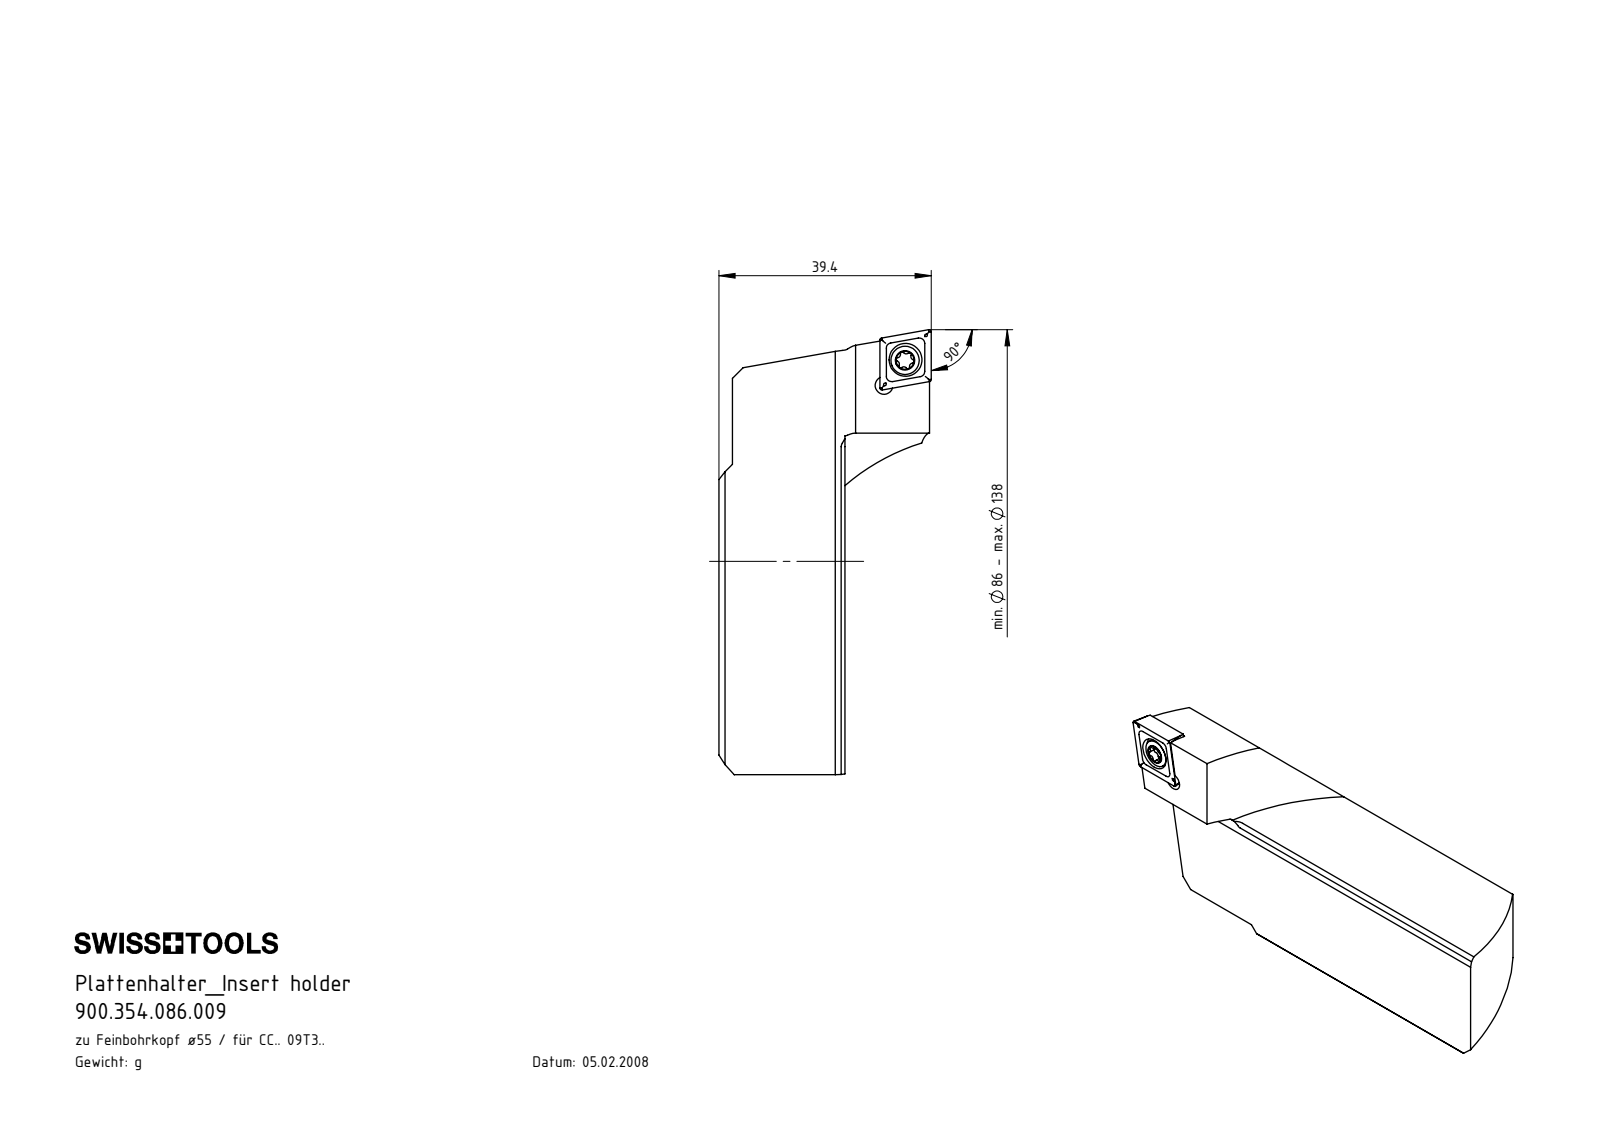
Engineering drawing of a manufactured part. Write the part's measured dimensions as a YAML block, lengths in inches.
part_name: "900.354.086.009; CCMT09T304; WCB-ER2.001.009_A; F00-WCB.086.001_C"
step_written_by: "SolidWorks 2017 (CONFIG_CONTROL_DESIGN)"
units: inches
bodies: {solids: 3, faces: 382, planar: 226, cylindrical: 39, other: 117}
overall_size: [3.251, 1.551, 1.077]
volume: 2.048
surface_area: 13.91
round_holes:
  - {diameter: 0.13, count: 2}
  - {diameter: 0.173, count: 1}
  - {diameter: 0.24, count: 1}
round_bosses_or_shafts:
  - {diameter: 0.207, count: 1}
  - {diameter: 0.157, count: 1}
partial_cylinders:
  - {radius: 0.008, count: 8}
  - {radius: 0.013, count: 6}
  - {radius: 0.023, count: 6}
  - {radius: 1.575, count: 3}
  - {radius: 0.031, count: 1}
face_to_face_distances: [0.094, 0.187, 0.839, 0.281, 0.375, 0.188, 0.281, 0.375, 0.469, 0.469]
hole_center_spacings: [0.239, 0.244]
